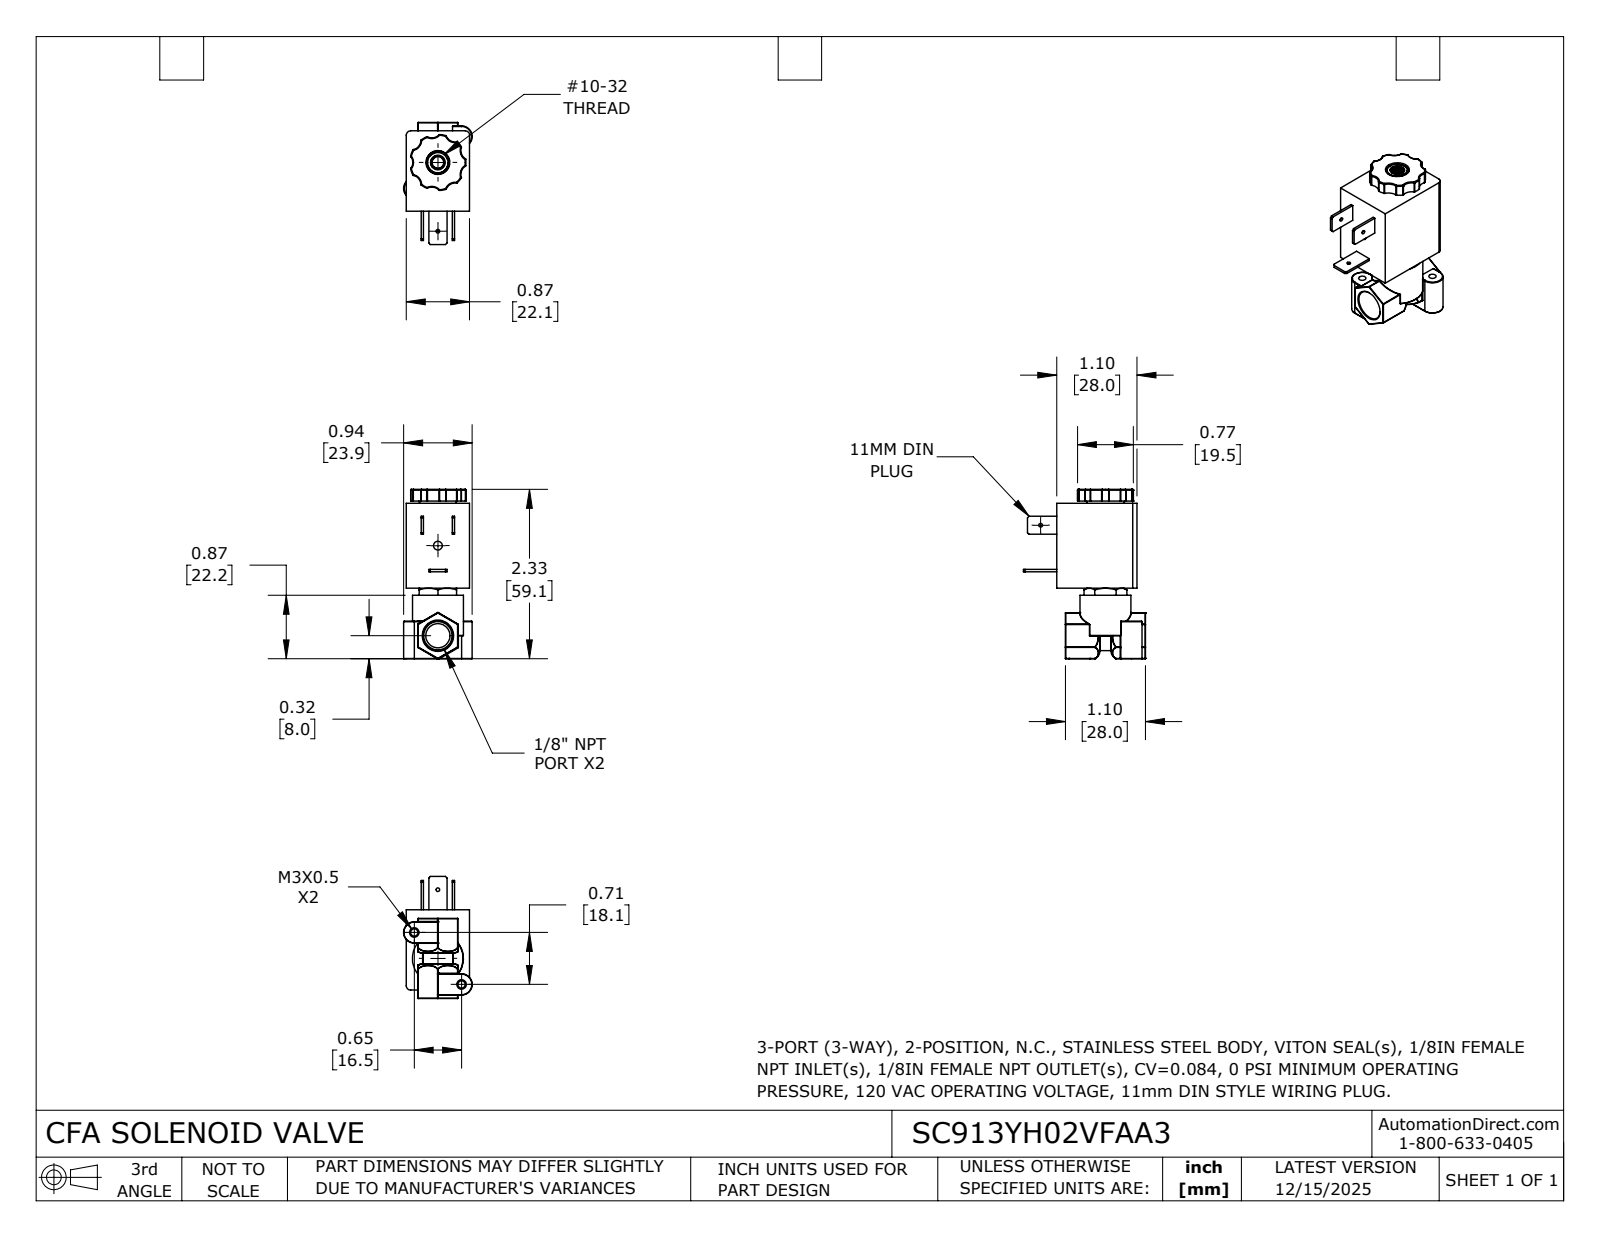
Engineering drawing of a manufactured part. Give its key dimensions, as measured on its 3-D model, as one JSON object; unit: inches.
{"part_name": "SC913YH02VFAA3", "step_written_by": "SolidWorks 2024 (CONFIG_CONTROL_DESIGN)", "units": "inches", "bodies": {"solids": 1, "faces": 363, "planar": 70, "cylindrical": 142, "other": 151}, "overall_size": [2.328, 1.678, 0.942], "volume_in3": 1.573, "surface_area_in2": 13.88, "round_holes": [[0.05, 2], [0.1, 2], [0.12, 1], [0.16, 1], [0.327, 1], [0.332, 1]], "round_bosses_or_shafts": [[0.7, 1], [0.315, 1]], "partial_cylinders_radius": [[0.004, 29], [0.01, 18], [0.008, 12], [0.133, 7], [0.017, 2], [0.06, 2], [0.132, 2], [0.146, 2]], "face_to_face_distances": [0.87, 1.104, 1.167, 0.548, 1.357, 0.19, 0.161, 0.709, 0.971, 2.138], "hole_center_spacings": [0.483, 0.672, 0.945, 0.965, 1.238, 1.342]}
